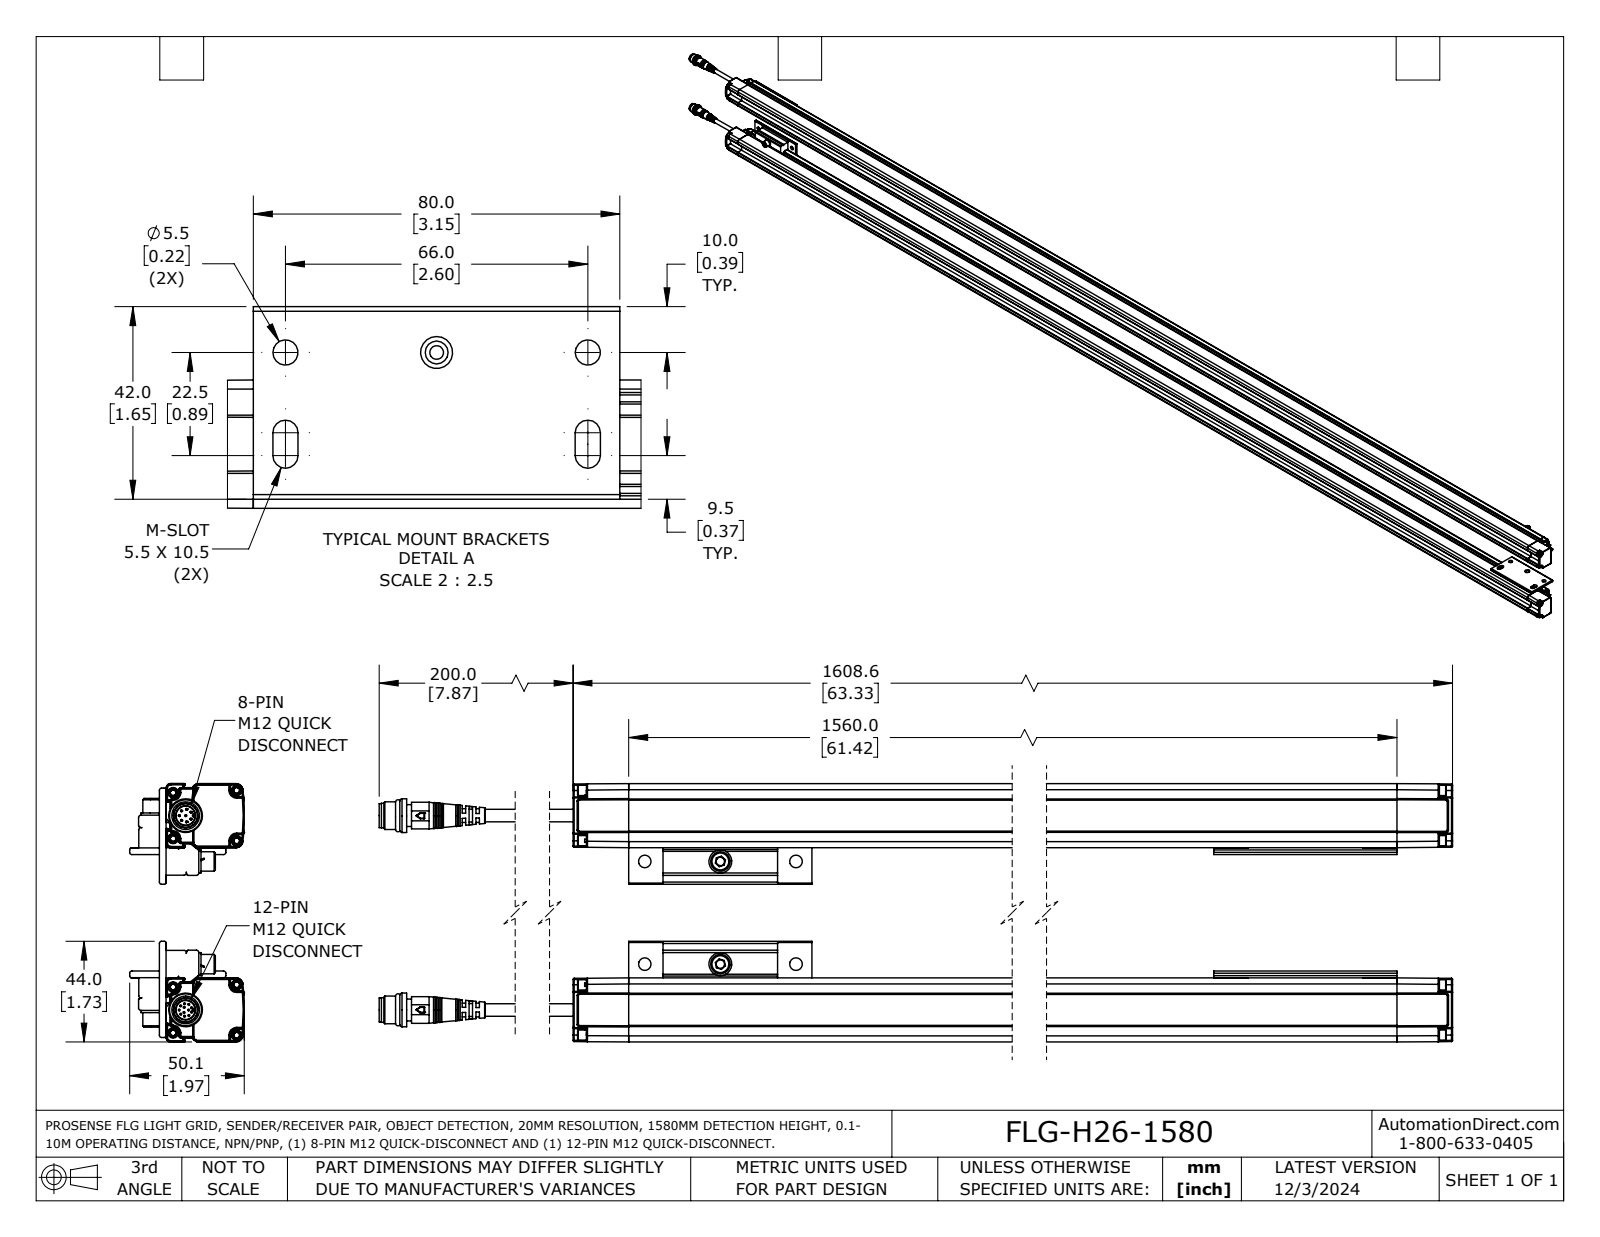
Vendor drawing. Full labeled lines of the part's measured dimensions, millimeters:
Part name (STEP PRODUCT): FLG-H26-1580
STEP written by: SolidWorks 2023 (AUTOMOTIVE_DESIGN)
Units: millimetres
Bodies: 11 solids, 1671 faces (818 planar, 456 cylindrical, 397 other)
Overall size (bounding box): 1700.55 × 112.8 × 50.09
Volume: 2 567 000 mm³ · Surface area: 620 577 mm²
Round holes (diameter × count): ⌀0.4 ×16, ⌀5.5 ×6, ⌀2.5 ×4, ⌀5 ×3, ⌀8.3 ×2
Round bosses / shafts (diameter × count): ⌀0.8 ×20, ⌀4.5 ×8, ⌀3 ×8, ⌀5.5 ×4, ⌀1.5 ×4, ⌀10 ×3, ⌀8.5 ×3, ⌀3.7 ×3
Partial cylindrical surfaces — rounded edges, fillets, slot ends (radius × count): R0.5 ×142, R1 ×40, R0.25 ×20, R0.2 ×12, R0.3 ×12, R2.75 ×12, R2.55 ×6, R1.25 ×4
Main face-to-face distances: 84.8, 28, 1.8, 7.25, 20.75, 24.65, 56.8, 112.8, 26.45, 5.45
Hole centre spacings: 2.75, 33, 4.15, 24.87, 55.64, 5.45, 44.8, 66
